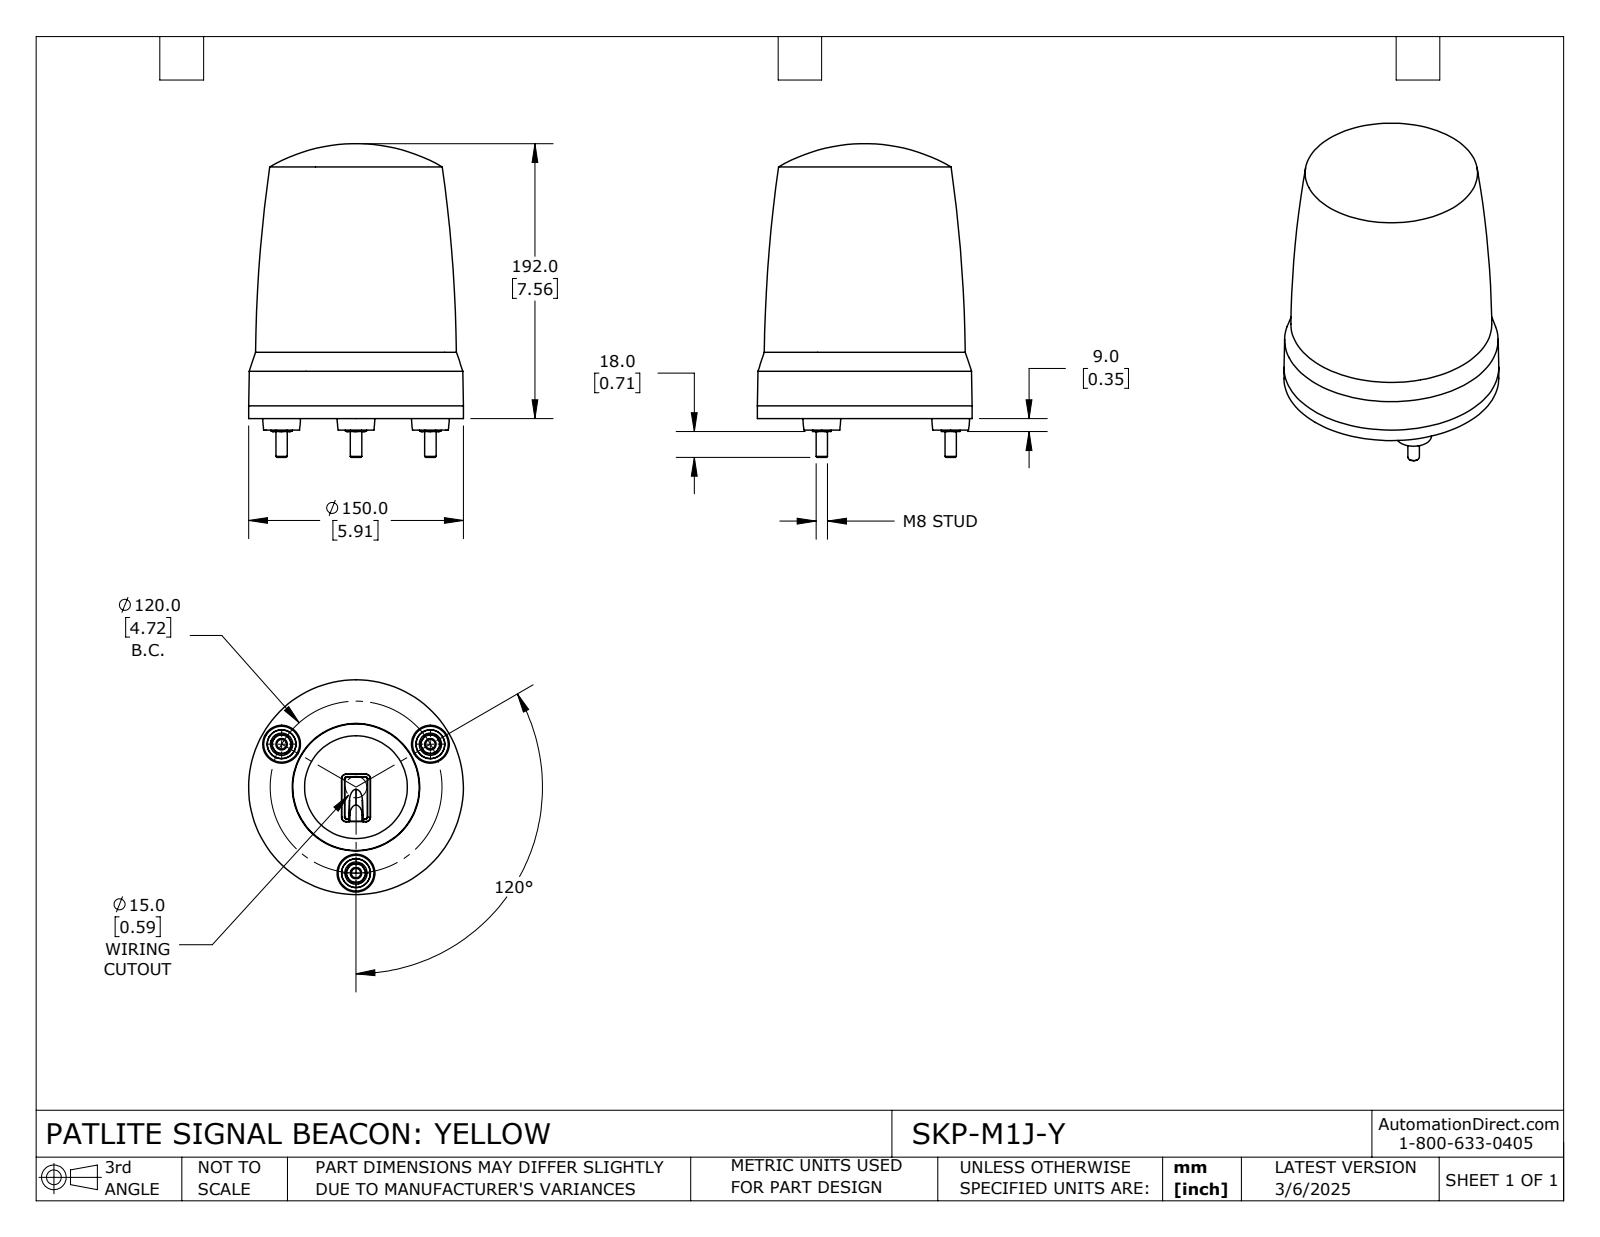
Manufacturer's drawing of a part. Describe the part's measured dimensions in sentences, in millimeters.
The part is named "SKP-M1J-Y". Its 3-D file was written by "SolidWorks 2024 (CONFIG_CONTROL_DESIGN)". It is 1 solid with 144 faces: 49 planar, 14 cylindrical and 81 other. Overall it measures 219 by 150 by 150 millimeters. Its volume is 2 538 000 cubic millimeters and its surface area 119 026 square millimeters. Round bosses or shafts: 3 of diameter 15.5, 3 of diameter 8, 1 of diameter 150. The main face-to-face distances are 32.7, 8, 40.7, 13, 7.1, 0.9, 33.6, 1.6, 36.05, 41.55.
